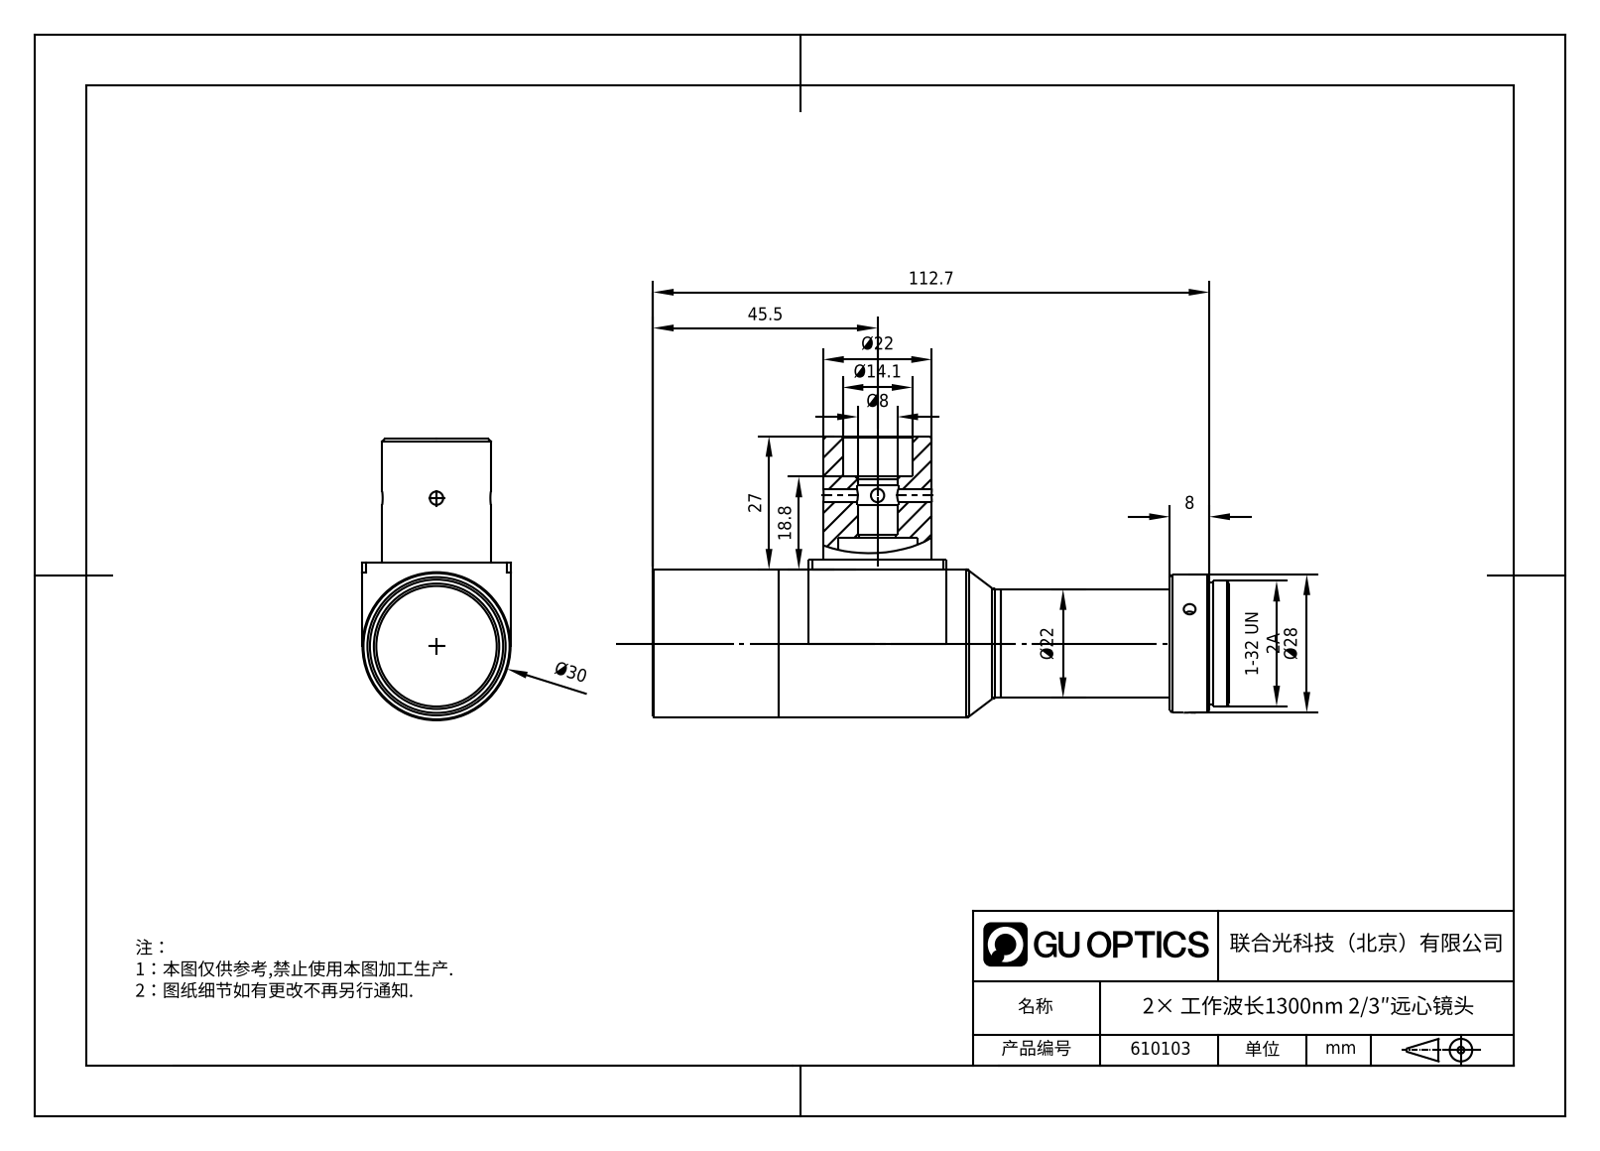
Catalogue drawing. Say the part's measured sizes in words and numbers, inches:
The part is named "610103". Its 3-D file was written by "SolidWorks 2020 (CONFIG_CONTROL_DESIGN)". It is 1 solid with 134 faces: 43 planar, 74 cylindrical and 17 other. Overall it measures 4.593 by 2.244 by 1.181 inches. Its volume is 4.994 cubic inches and its surface area 23.48 square inches. Round holes: 4 of diameter 0.063, 4 of diameter 0.091, 3 of diameter 0.094, 2 of diameter 0.106, 1 of diameter 0.807, 1 of diameter 1.122. Round bosses or shafts: 2 of diameter 0.866, 1 of diameter 1.181, 1 of diameter 1.102, 1 of diameter 1.098, 1 of diameter 1, 1 of diameter 0.969, 1 of diameter 0.787, 1 of diameter 0.774. Partial cylindrical surfaces (rounded edges, fillets, slot ends): 8 of radius 0.079, 4 of radius 0.059, 1 of radius 0.343, 1 of radius 0.382, 1 of radius 0.458, 1 of radius 0.471, 1 of radius 0.787. The main face-to-face distances are 1.181, 4.593, 0.984, 0.472, 4.12, 2.252, 1.779, 2.341, 3.354, 2.881. The hole center spacings are 0.866, 0.945, 1.282, 2.108, 2.959, 1.181.
